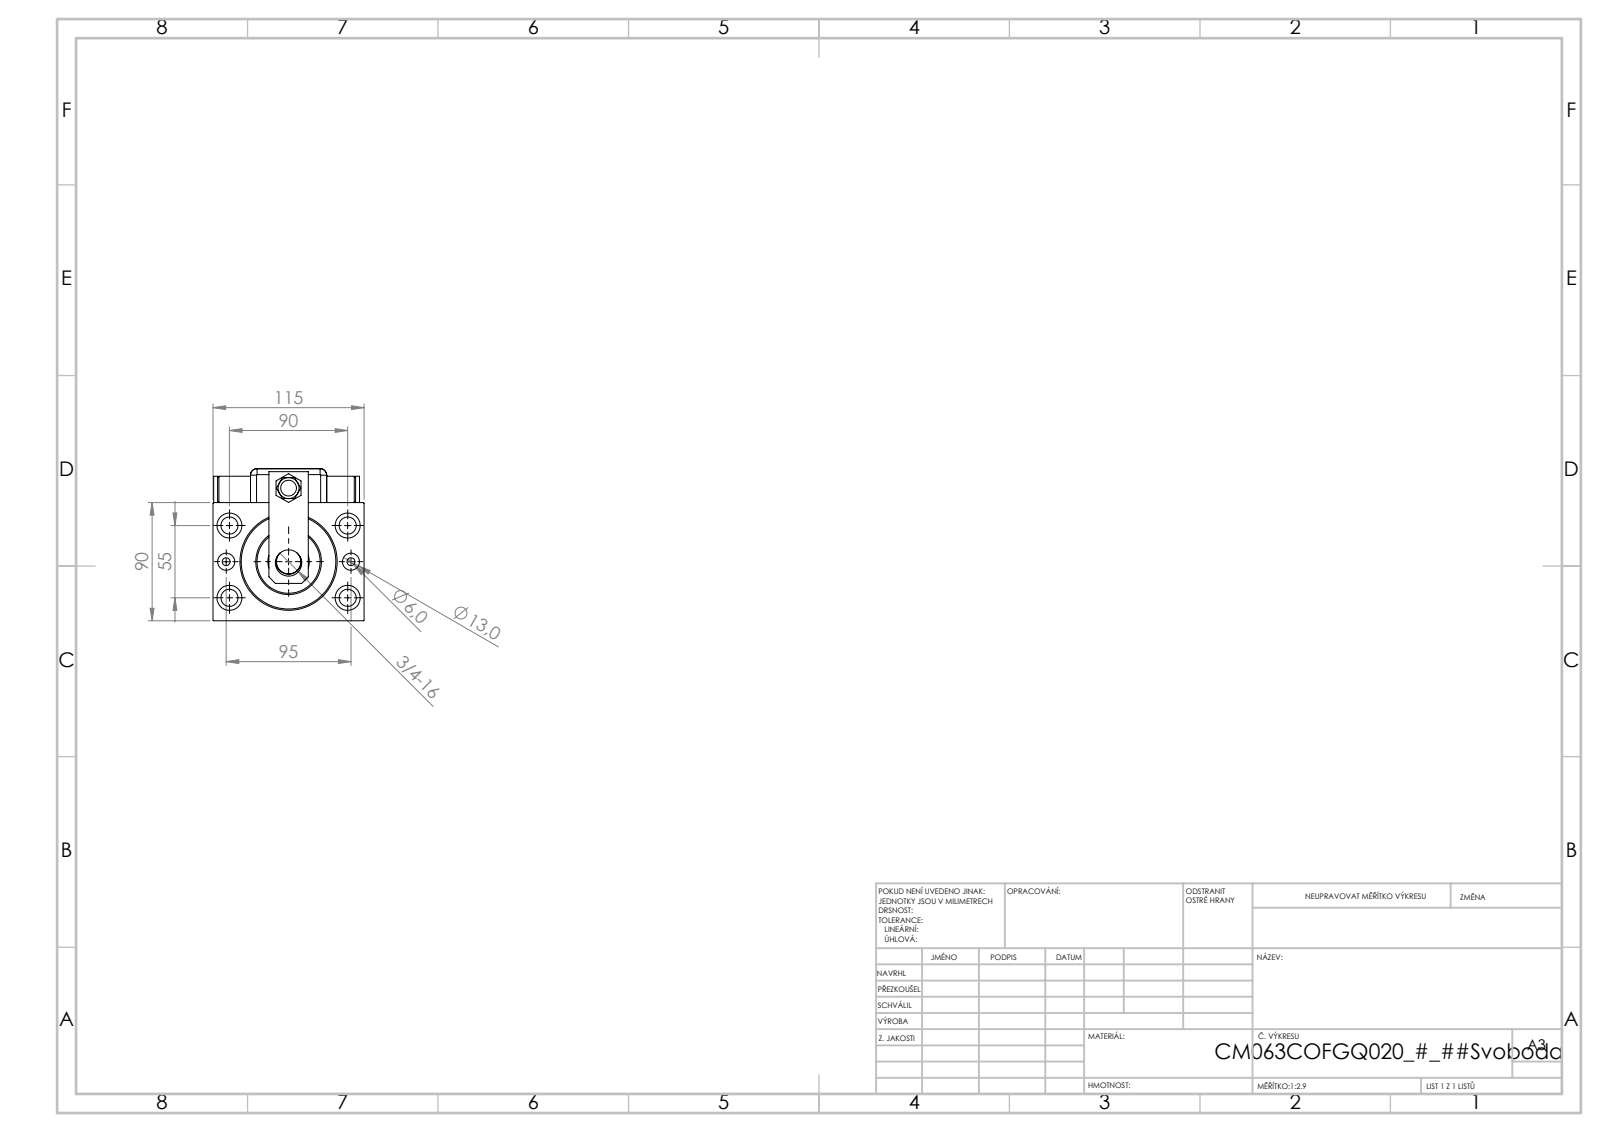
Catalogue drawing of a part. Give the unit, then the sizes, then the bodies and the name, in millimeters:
Units: millimetres
Overall size (bounding box): 150.46 × 115.8 × 115
Round holes (diameter × count): ⌀13 ×7, ⌀19 ×4, ⌀4 ×2, ⌀6 ×2, ⌀8 ×2, ⌀12 ×1, ⌀14 ×1, ⌀18.5 ×1, ⌀20 ×1, ⌀28 ×1, ⌀31.5 ×1, ⌀63 ×1
Round bosses / shafts (diameter × count): ⌀20 ×3, ⌀16 ×2, ⌀14 ×2, ⌀6 ×2, ⌀50 ×1
Partial cylindrical surfaces — rounded edges, fillets, slot ends (radius × count): R5 ×9, R10 ×1, R13.5 ×1
Main face-to-face distances: 90, 3, 115, 98, 51, 47, 110, 20, 8, 25.8
Hole centre spacings: 27.61, 52.74, 53.27, 96.5, 47.5, 47.51, 52.22, 55
Volume: 1 063 000 mm³ · Surface area: 174 606 mm²
Bodies: 13 solids, 1245 faces (615 planar, 113 cylindrical, 517 other)
Part name (STEP PRODUCT): V450CM_VC_B; SWITCH_Q_FRONT_BACK; NUT_D13; TYC (+7 more)
STEP written by: SolidWorks 2019 (CONFIG_CONTROL_DESIGN)
